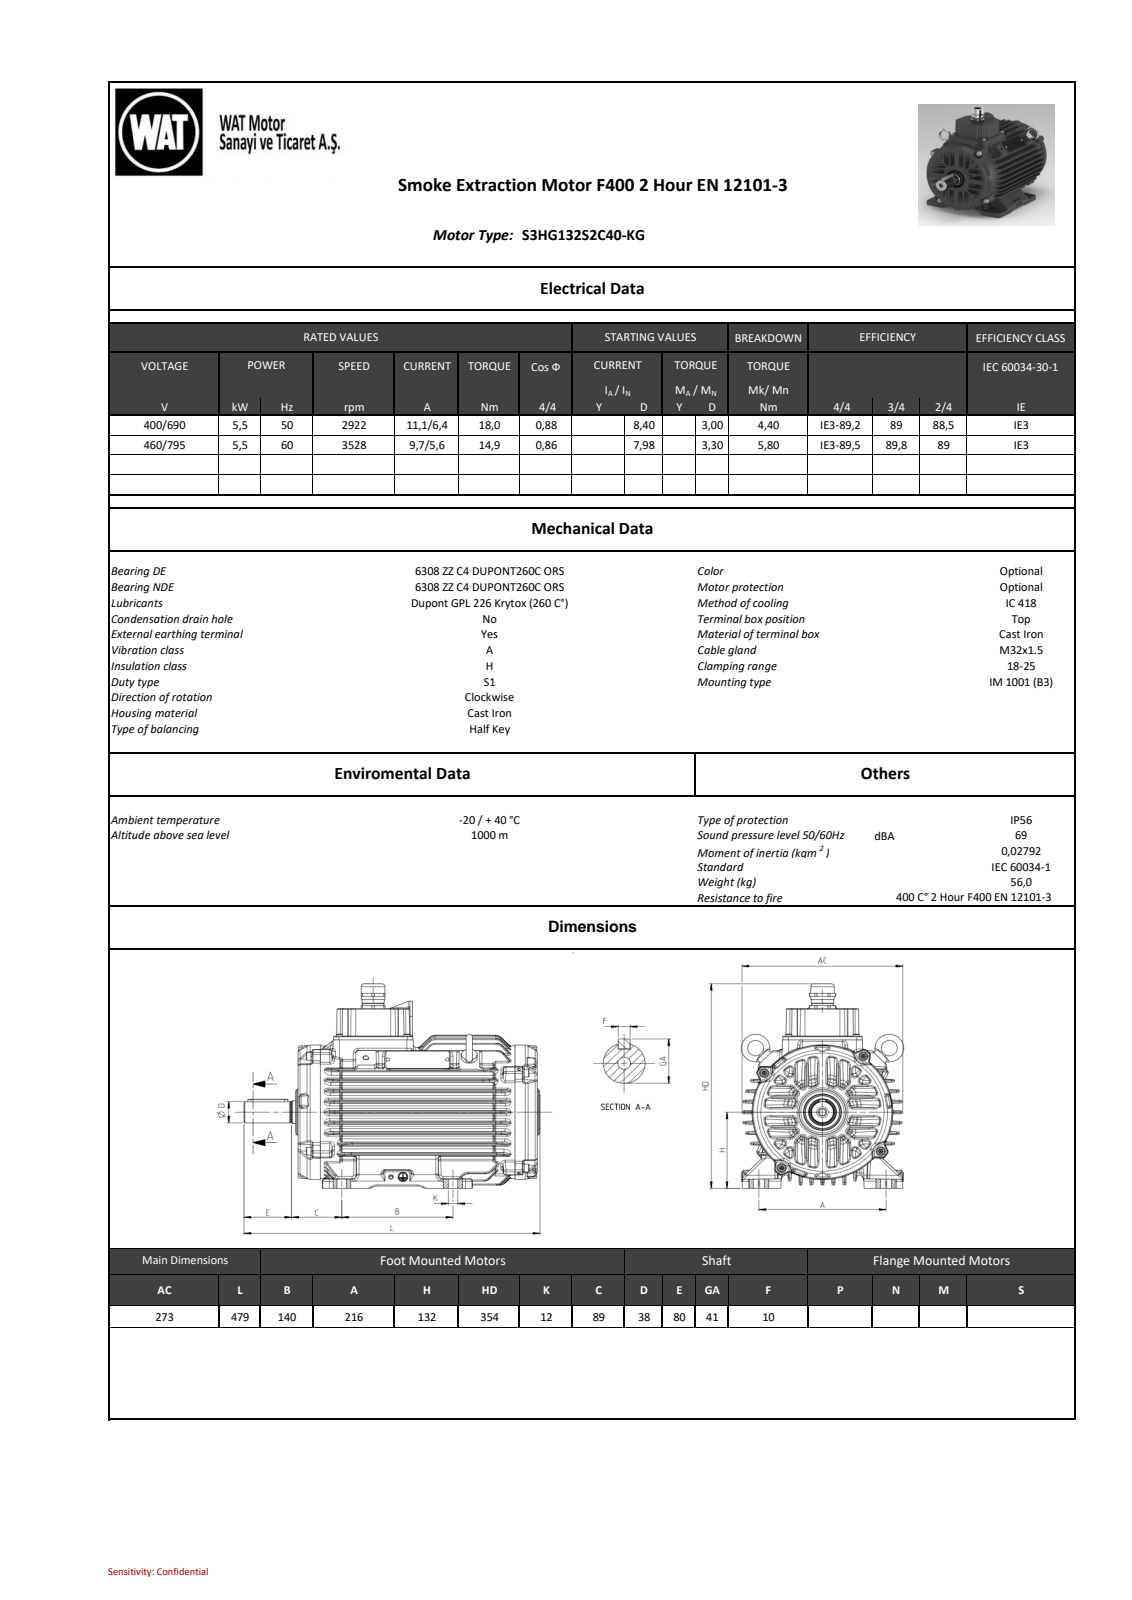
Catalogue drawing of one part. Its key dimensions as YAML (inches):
part_name: "26032C0836B7xj3q"
step_written_by: "SIEMENS PLM Software NX 11.0 (AUTOMOTIVE_DESIGN)"
units: inches
bodies: {solids: 0, faces: 6810, planar: 848, cylindrical: 1480, other: 4482}
overall_size: [18.858, 13.957, 11.008]
round_holes:
  - {diameter: 0.268, count: 8}
  - {diameter: 0.13, count: 4}
  - {diameter: 0.098, count: 2}
  - {diameter: 0.335, count: 2}
  - {diameter: 0.197, count: 1}
  - {diameter: 0.406, count: 1}
  - {diameter: 0.512, count: 1}
  - {diameter: 0.984, count: 1}
  - {diameter: 1.732, count: 1}
  - {diameter: 2.299, count: 1}
  - {diameter: 2.307, count: 1}
round_bosses_or_shafts:
  - {diameter: 0.501, count: 8}
  - {diameter: 0.583, count: 6}
  - {diameter: 0.394, count: 4}
  - {diameter: 0.787, count: 2}
  - {diameter: 9.409, count: 1}
  - {diameter: 2.441, count: 1}
  - {diameter: 1.574, count: 1}
  - {diameter: 1.559, count: 1}
partial_cylinders:
  - {radius: 0.157, count: 307}
  - {radius: 0.118, count: 179}
  - {radius: 0.079, count: 148}
  - {radius: 0.059, count: 106}
  - {radius: 0.071, count: 64}
  - {radius: 0.236, count: 33}
  - {radius: 0.197, count: 32}
  - {radius: 0.02, count: 13}
face_to_face_distances: [2.202, 0.542, 0.544, 1.086, 4.338, 3.252, 3.793, 1.633, 1.092, 0.547]
hole_center_spacings: [4.783, 6.765, 1.661, 5.487, 7.837, 9.422, 9.567, 1.398]
